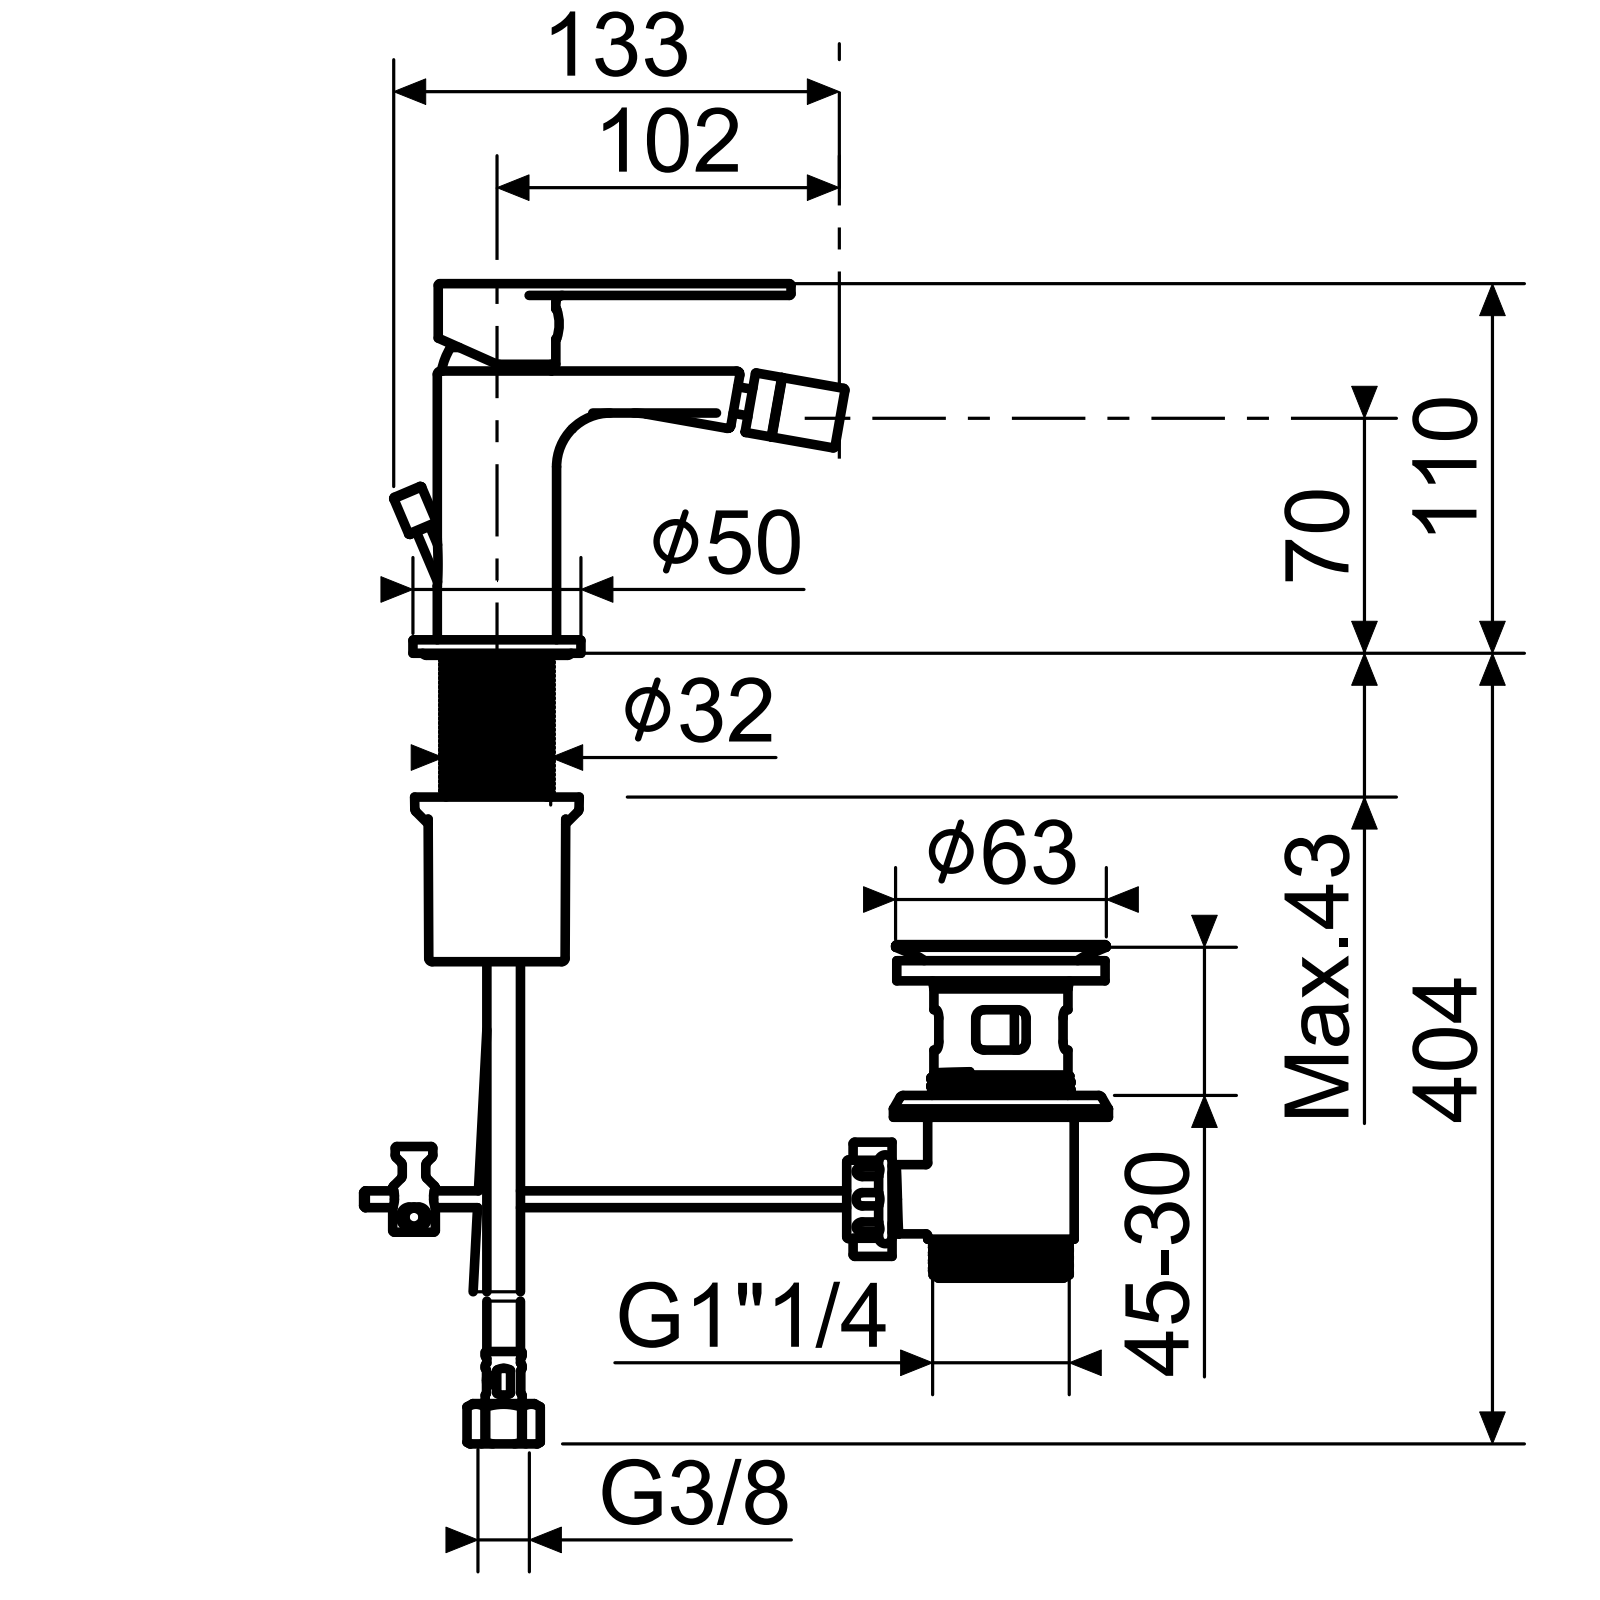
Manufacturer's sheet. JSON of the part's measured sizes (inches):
{"part_name": "AUNO300C002; SFDMAC0001; SVGMAC0008; SORMAC0019 (+8 more)", "step_written_by": "CREO PARAMETRIC BY PTC INC, 2022164 (CONFIG_CONTROL_DESIGN)", "units": "inches", "bodies": {"solids": 65, "faces": 5727, "planar": 2416, "cylindrical": 1641, "other": 1670}, "overall_size": [21.969, 21.641, 3.661], "volume_in3": 69.45, "surface_area_in2": 1744, "round_holes": [[0.394, 5], [0.236, 4], [0.354, 4], [0.118, 3], [0.177, 3], [0.256, 3], [0.165, 2], [0.173, 2], [0.197, 2], [0.217, 2], [0.276, 2], [0.315, 2]], "round_bosses_or_shafts": [[0.433, 5], [0.276, 5], [0.386, 4], [0.236, 4], [0.984, 2], [0.551, 2], [0.531, 2], [0.472, 2]], "partial_cylinders_radius": [[0.02, 112], [0.039, 77], [0.012, 30], [0.008, 25], [0.059, 22], [0.079, 19], [0.098, 15], [0.118, 15]], "face_to_face_distances": [0.079, 2.283, 0.315, 1.406, 1.72, 0.878, 0.563, 2.362, 2.205, 0.236], "hole_center_spacings": [0.249, 0.713, 0.472, 0.088, 0.251, 0.252, 0.287, 0.352]}
